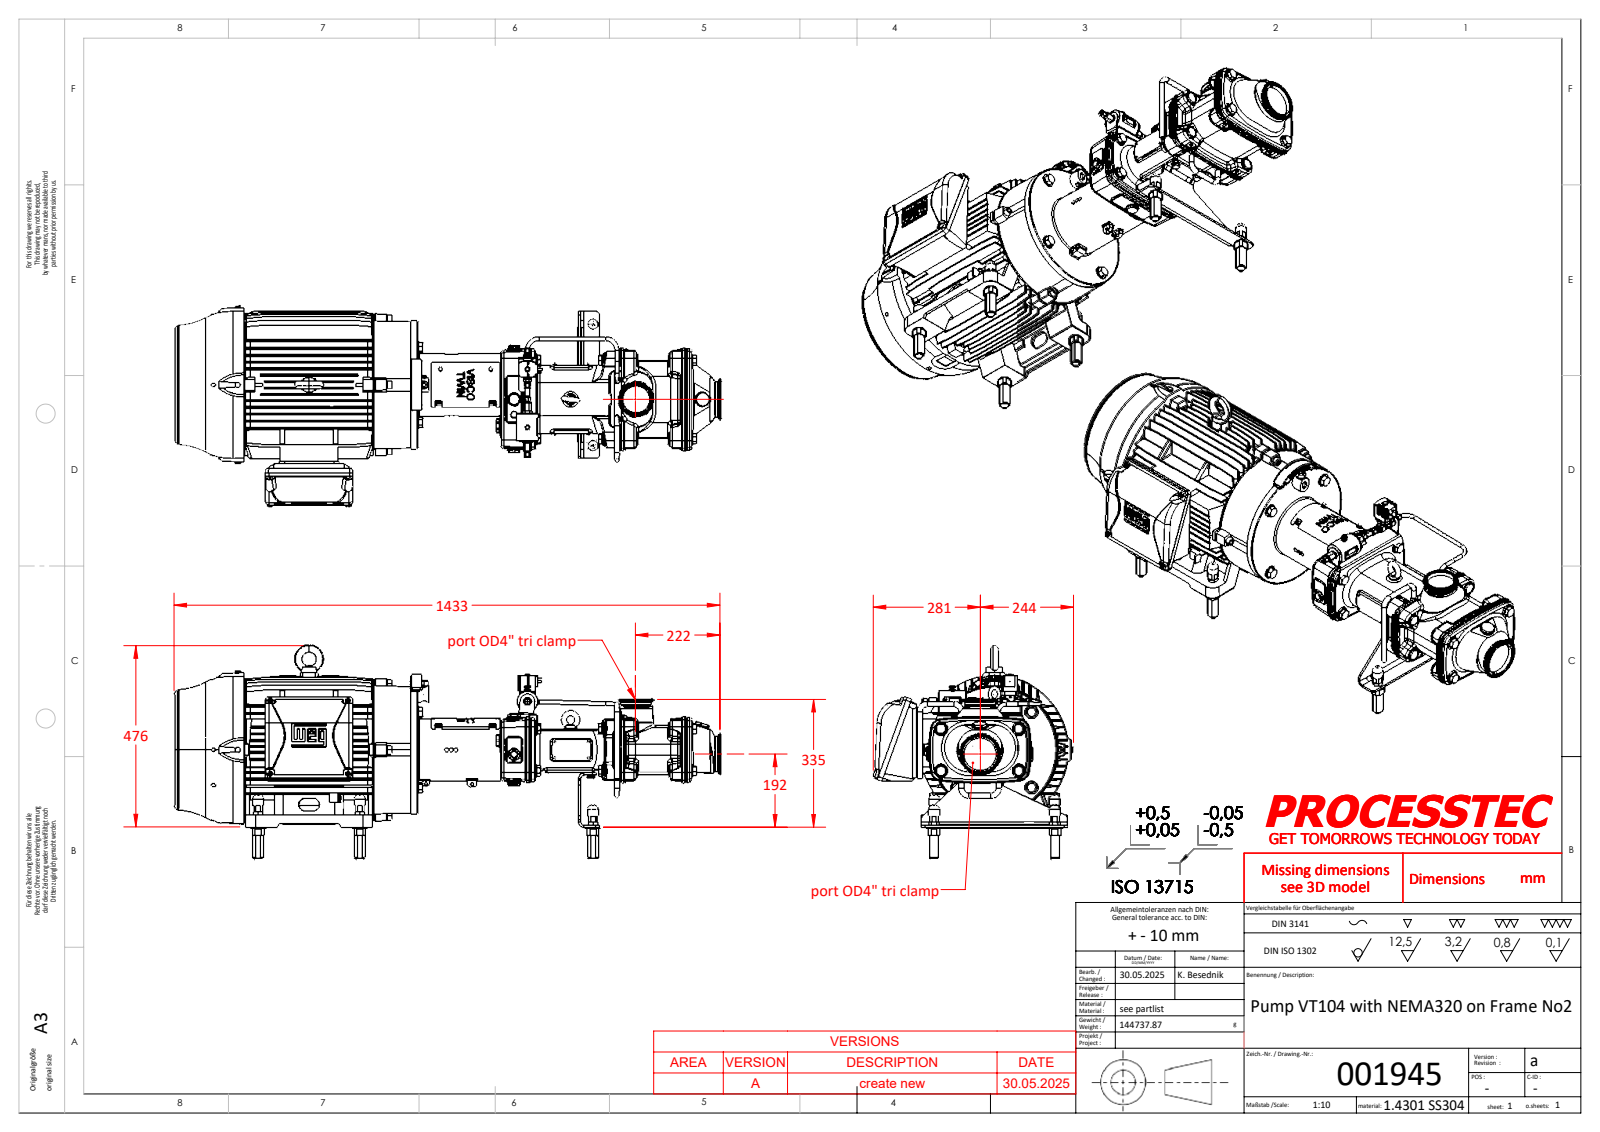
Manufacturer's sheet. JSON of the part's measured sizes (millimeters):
{"part_name": "001187_Washer ISO 7089 - 10; 001090_ISO 2338 - 8 h8 x 20 - A1; 001946_M16 middle; 001269 (+8 more)", "step_written_by": "SolidWorks 2023 (AUTOMOTIVE_DESIGN)", "units": "millimeters", "bodies": {"solids": 106, "faces": 8820, "planar": 3038, "cylindrical": 2572, "other": 3210}, "overall_size": [1433.05, 557.2, 525.98], "volume_mm3": 82730000, "surface_area_mm2": 4724000, "round_holes": [[8, 21], [14, 11], [6.8, 8], [8.5, 8], [16, 8], [25.2, 6], [4.35, 5], [5, 5], [9, 5], [17.5, 5], [18, 5], [2.5, 4]], "round_bosses_or_shafts": [[10, 9], [8, 9], [24, 8], [25, 7], [11.6, 7], [34, 6], [16, 5], [33.32, 4]], "partial_cylinders_radius": [[2.98, 188], [2, 60], [5, 58], [3, 42], [1.5, 39], [8, 34], [6, 24], [4, 21]], "face_to_face_distances": [342.3, 102, 444.3, 747.8, 405.5, 303.5, 175.65, 517.95, 619.95, 923.45], "hole_center_spacings": [55, 193.35, 266.7, 28.75, 67.98, 94.4, 101.37, 107.22]}
